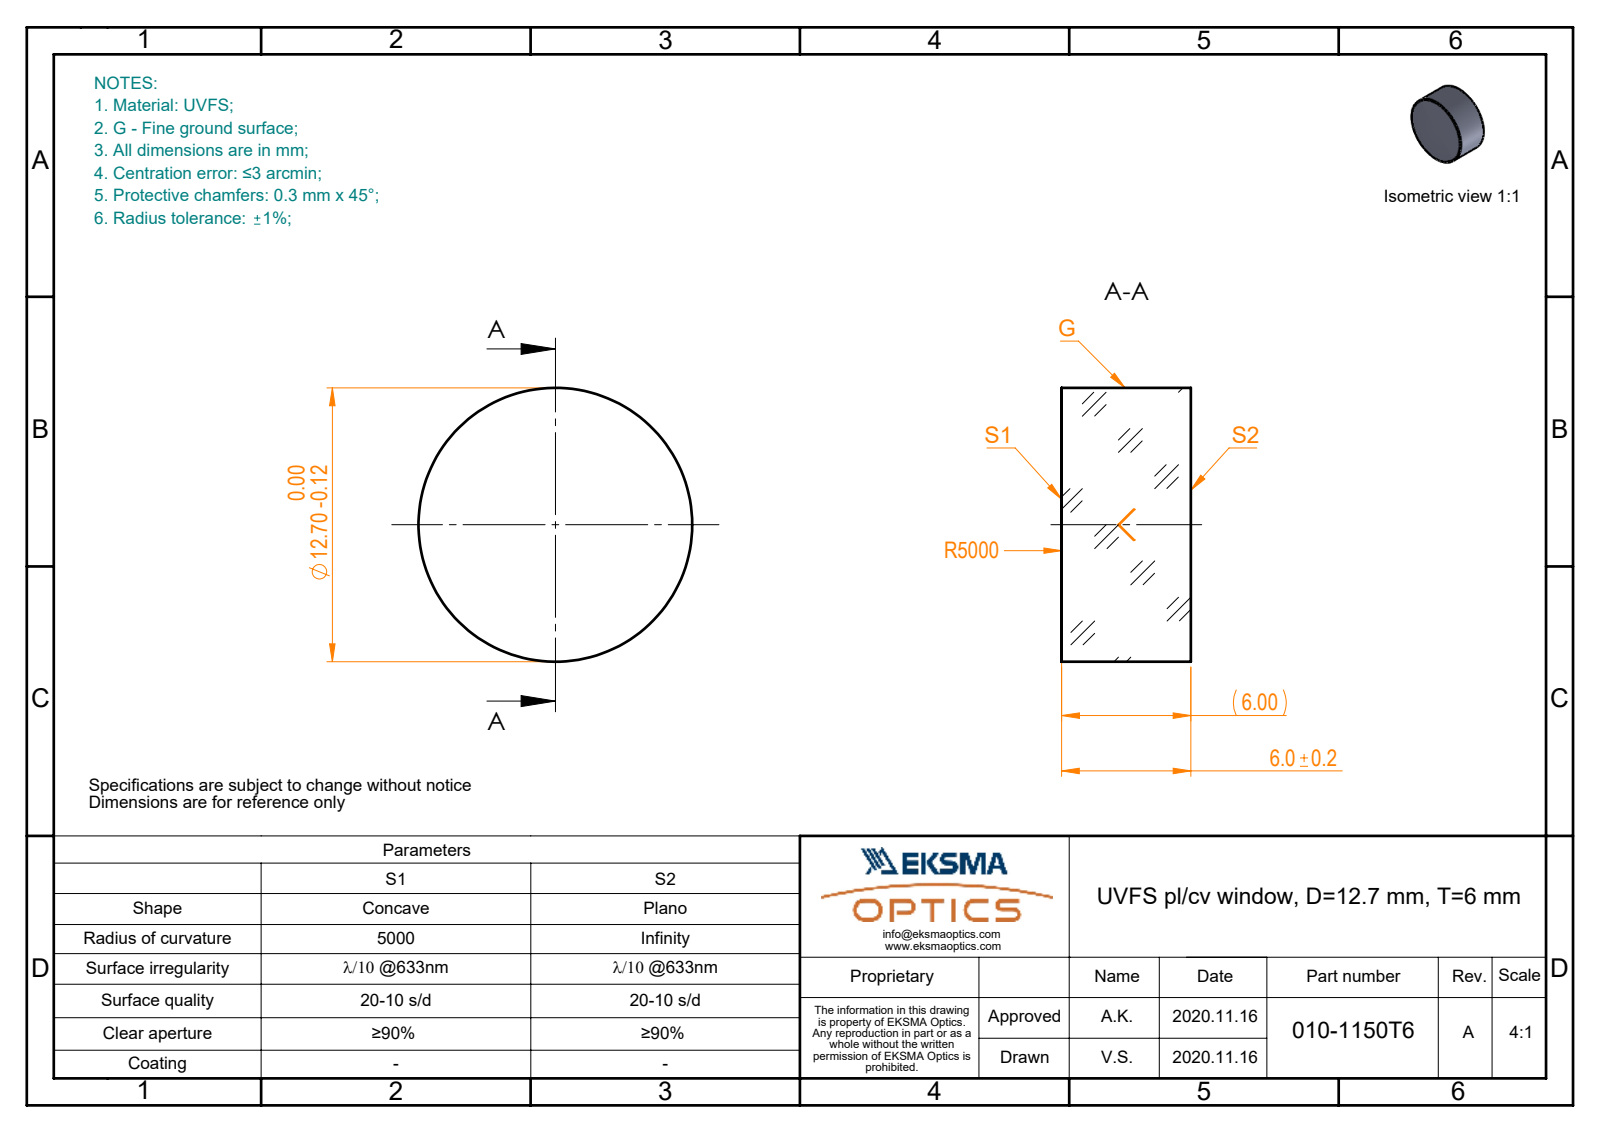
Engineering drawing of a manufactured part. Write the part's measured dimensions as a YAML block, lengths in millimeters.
part_name: "010-1150T6_UVFS_PCV_window"
step_written_by: "SolidWorks 2019 (CONFIG_CONTROL_DESIGN)"
units: millimeters
bodies: {solids: 1, faces: 5, planar: 1, cylindrical: 2, other: 2}
overall_size: [12.7, 12.7, 6]
volume: 760
surface_area: 493
round_bosses_or_shafts:
  - {diameter: 12.7, count: 1}
